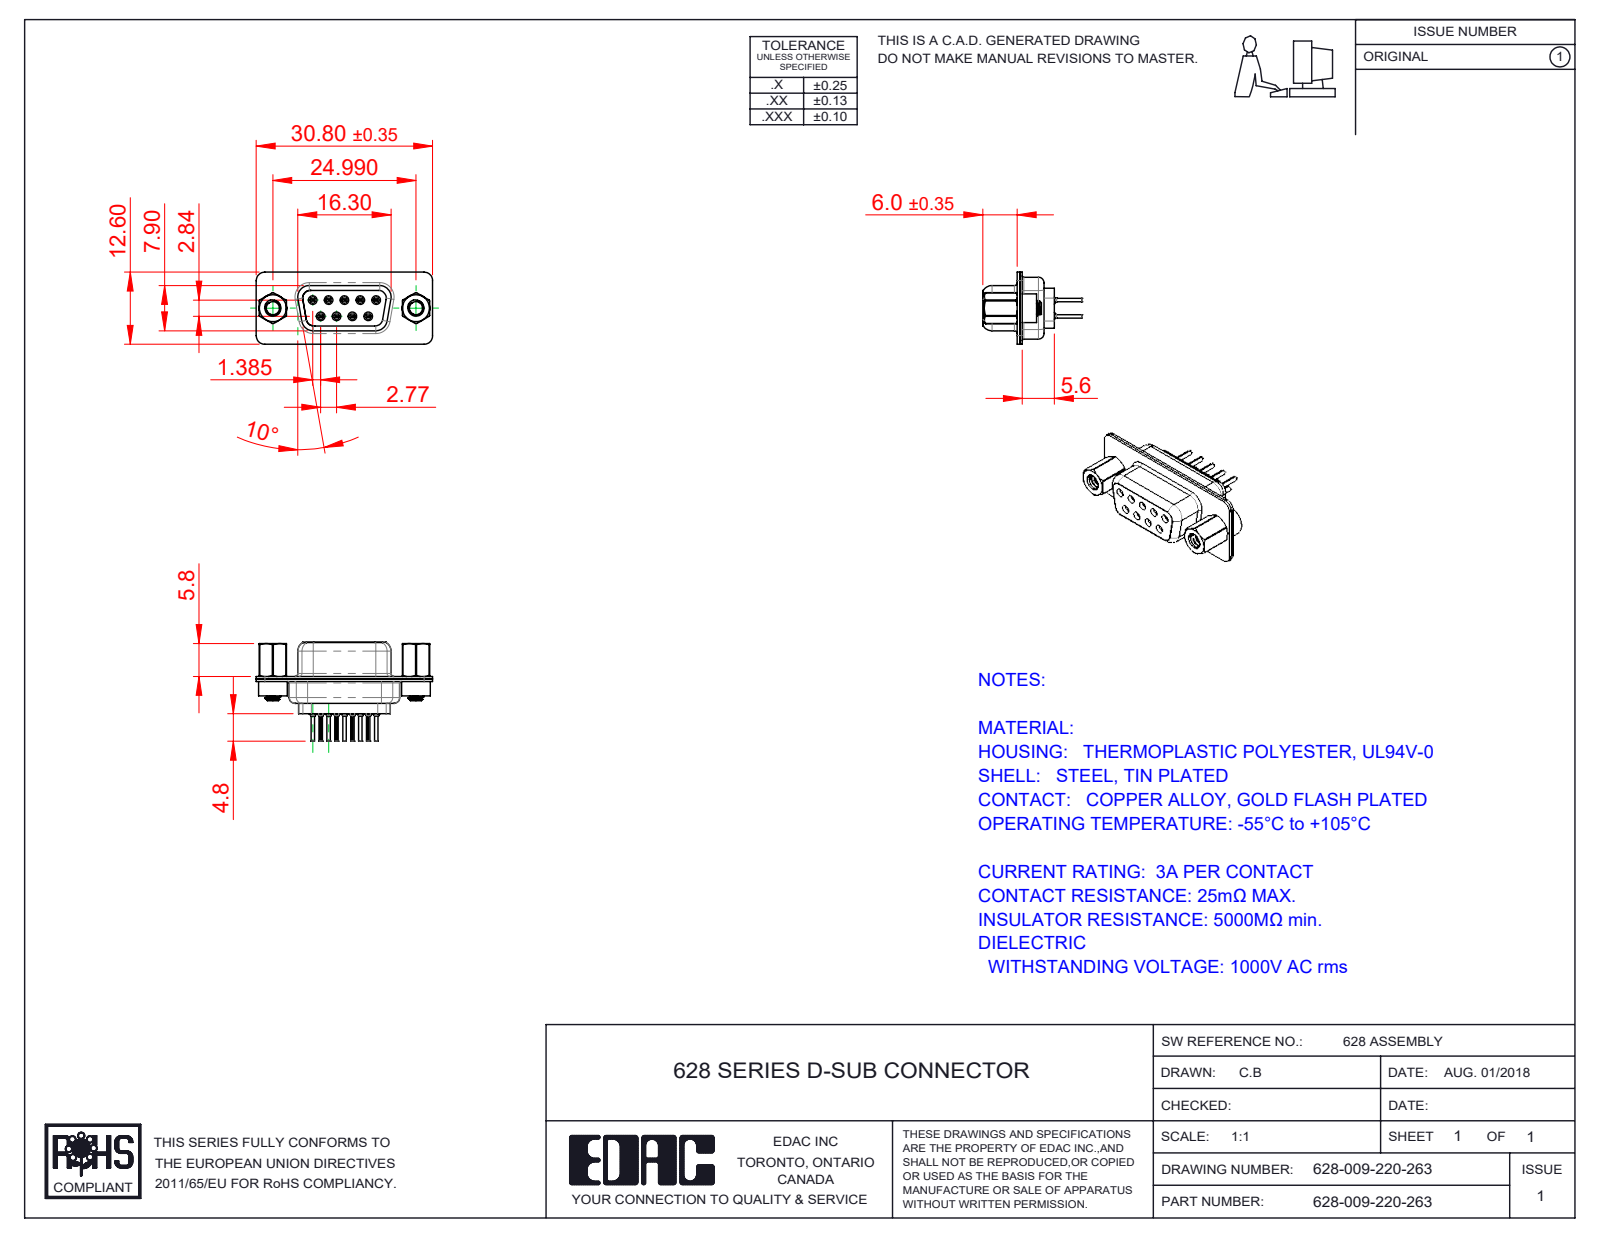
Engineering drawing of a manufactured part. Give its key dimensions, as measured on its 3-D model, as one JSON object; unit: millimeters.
{"part_name": "628 Shell Front_09 Contacts; 628 4-40 Threaded Rivet; 628 Contact Row 1_20L; 628-009-220-263 (+4 more)", "step_written_by": "SolidWorks 2020 (CONFIG_CONTROL_DESIGN)", "units": "millimeters", "bodies": {"solids": 16, "faces": 1544, "planar": 368, "cylindrical": 504, "other": 672}, "overall_size": [30.8, 17.3, 12.6], "volume_mm3": 1966, "surface_area_mm2": 4980, "round_holes": [[0.2, 9], [0.8, 9], [0.9, 9], [1.1, 9], [1.6, 9], [1.7, 5], [2.26, 2], [2.29, 2], [4, 2], [4.05, 2], [4.85, 2]], "round_bosses_or_shafts": [[2, 9], [1.5, 9], [1.2, 9], [0.6, 9], [5, 2], [4.95, 2], [4.8, 2], [2.79, 2]], "partial_cylinders_radius": [[0.1, 18], [1.5, 17], [2, 12], [0.28, 9], [1.35, 6], [0.25, 4], [0.5, 4], [0.6, 4]], "face_to_face_distances": [0.45, 0.4, 0.9, 1.9, 8.5, 6.6, 1.4, 0.5, 12.5, 6.2], "hole_center_spacings": [3.16, 2.77, 5.54, 5.03, 5.04, 8.31, 7.48, 7.49]}
